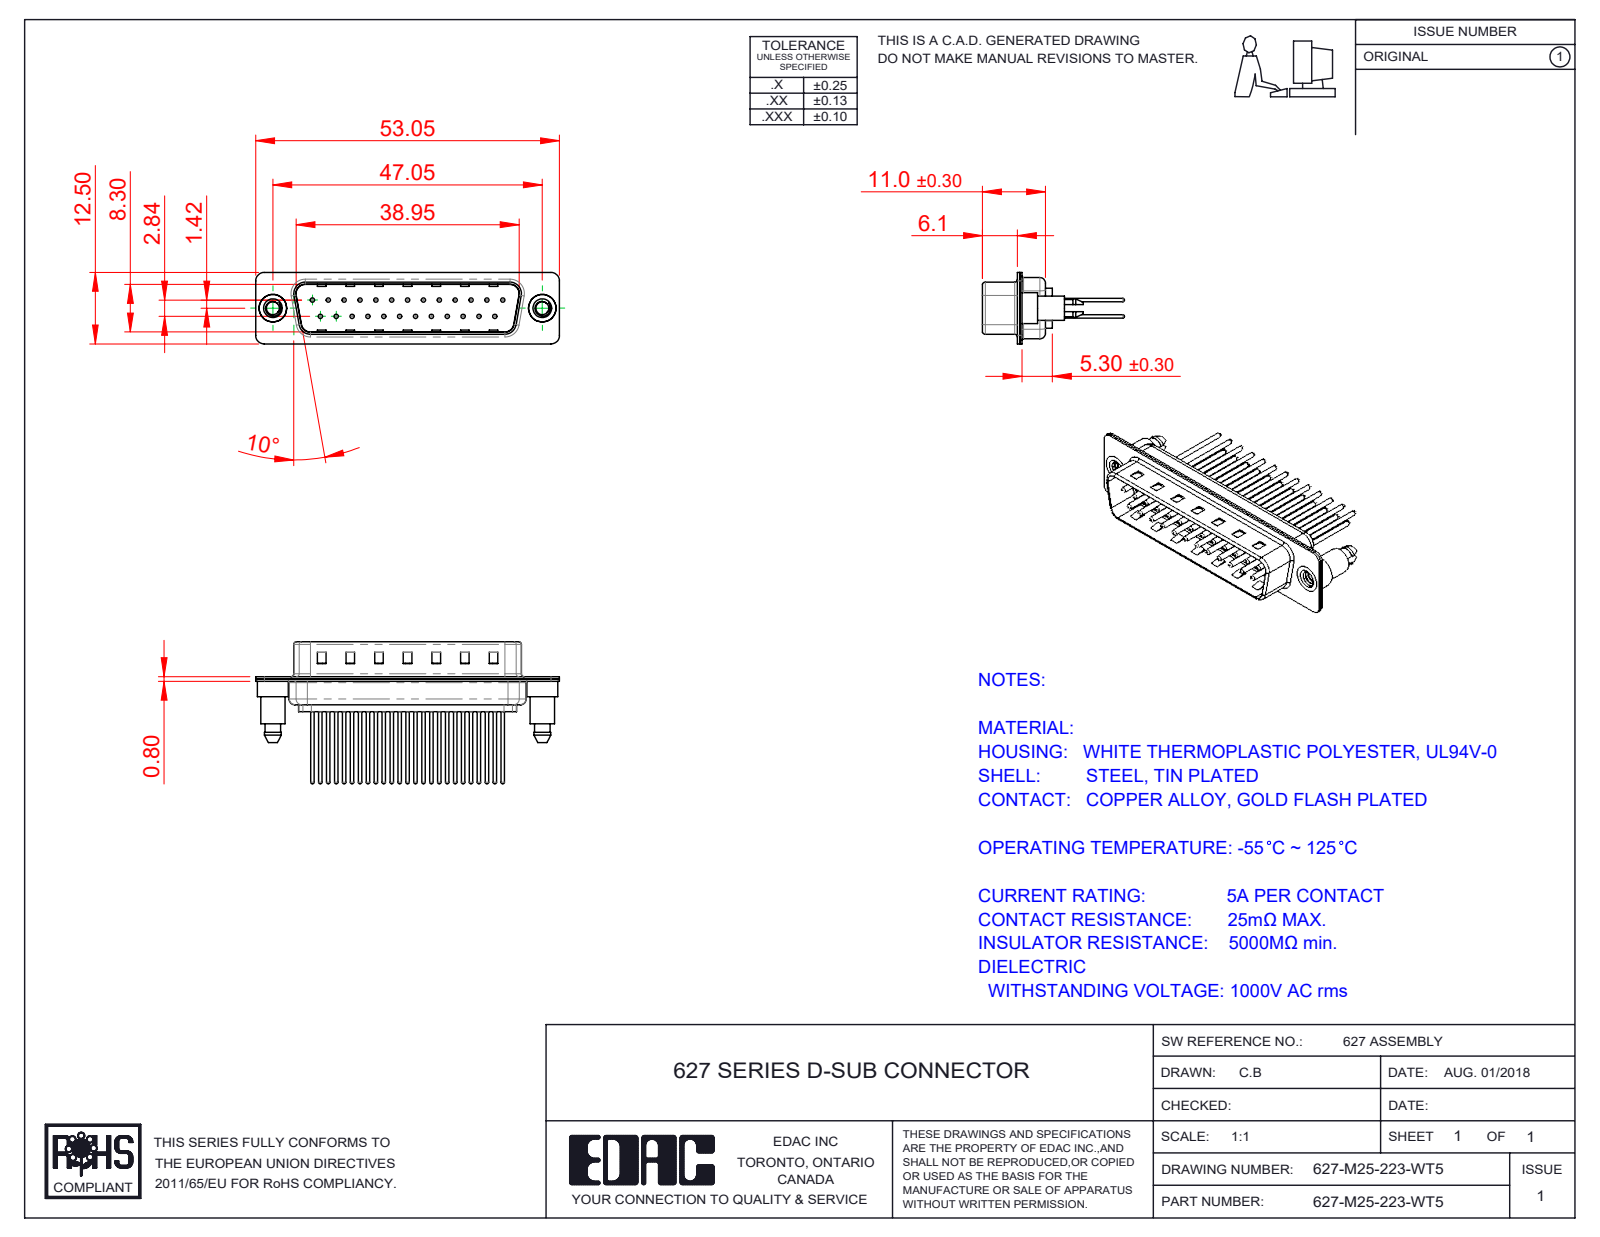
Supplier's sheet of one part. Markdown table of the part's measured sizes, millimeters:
| quantity | value |
| --- | --- |
| part name | 627-M25-223-WT5; 627M Shell Front_25 Contacts; 627M Housing_25 Contacts; 627M Contact Row 2_23 (+3 more) |
| STEP written by | SolidWorks 2020 (CONFIG_CONTROL_DESIGN) |
| units | millimeters |
| bodies | 30 solids, 1351 faces (362 planar, 519 cylindrical, 470 other) |
| overall size | 53.05 × 24.77 × 12.5 |
| volume | 2 901 mm³ |
| surface area | 7 500 mm² |
| round holes (diameter × count) | 0.75 × 25, 1.6 × 25, 2 × 25, 2.26 × 2, 4 × 2, 4.8 × 2 |
| round bosses / shafts (diameter × count) | 1.5 × 25, 0.6 × 25, 5.4 × 2, 4.9 × 2, 4.25 × 2 |
| partial cylindrical surfaces (radius × count) | 1.5 × 18, 2 × 12, 1.6 × 10, 0.5 × 8, 0.25 × 4, 0.6 × 4, 0.65 × 4, 0.9 × 4 |
| main face-to-face distances | 0.4, 0.8, 9.5, 9.1, 8.7, 9.9, 1.2, 6.1, 5.7, 0.75 |
| hole center spacings | 3.16, 2.77, 5.54, 8.31, 11.08, 13.85, 16.62, 5.03 |
